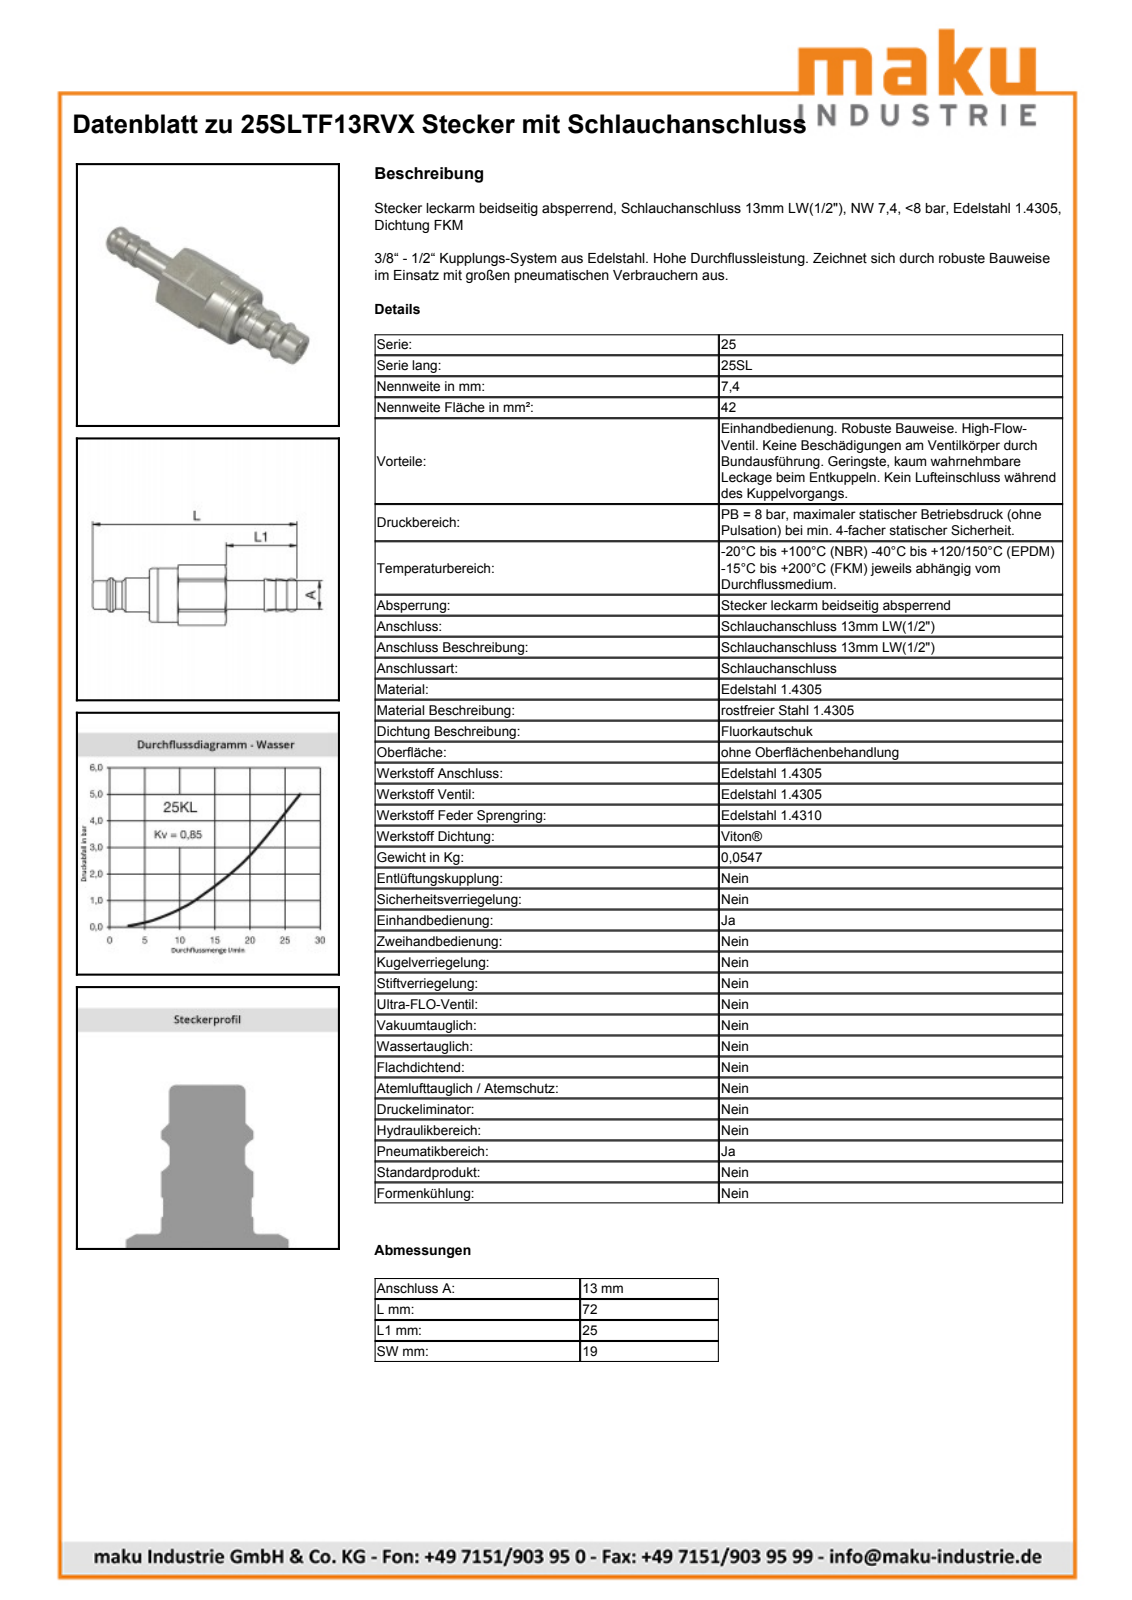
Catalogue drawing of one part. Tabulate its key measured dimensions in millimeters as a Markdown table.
| quantity | value |
| --- | --- |
| part name | D106657 |
| STEP written by | Autodesk Inventor 2011 (AUTOMOTIVE_DESIGN) |
| units | millimeters |
| bodies | 1 solid, 57 faces (16 planar, 18 cylindrical, 23 other) |
| overall size | 72 × 21.3 × 20.22 |
| volume | 13 455 mm³ |
| surface area | 4 819 mm² |
| round holes (diameter × count) | 15.1 × 1, 16 × 1 |
| round bosses / shafts (diameter × count) | 19 × 1, 18.95 × 1, 14.83 × 1, 14.5 × 1, 13.1 × 1, 12 × 1, 9.9 × 1, 9.75 × 1 |
| partial cylindrical surfaces (radius × count) | 10.7 × 1 |
| main face-to-face distances | 19, 25, 27, 52, 20, 47, 72, 27.5, 7.5, 19.5 |
